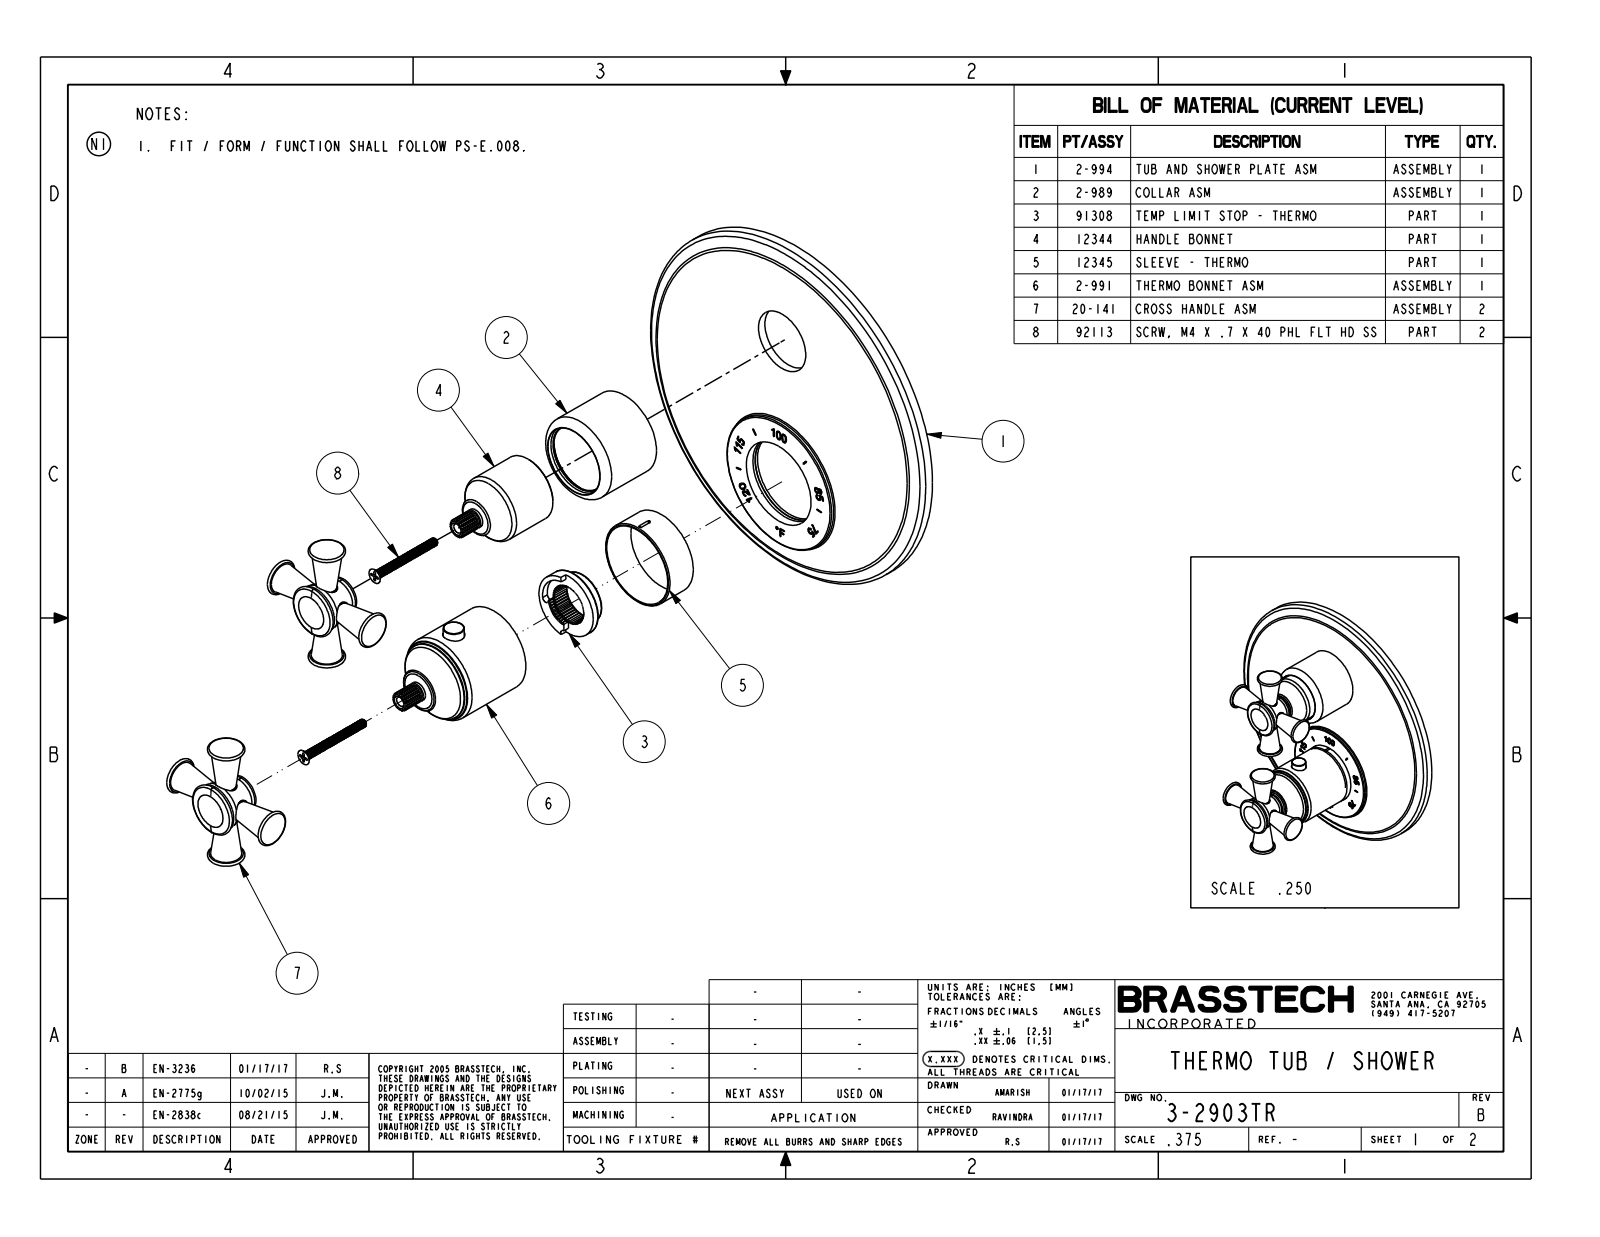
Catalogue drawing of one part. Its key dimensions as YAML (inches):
part_name: "12346_AF0; H-78_2_FEET_AF1; 91678; 2-994_AF0_ASM (+8 more)"
step_written_by: "PRO/ENGINEER BY PARAMETRIC TECHNOLOGY CORPORATION, 2013150 (CONFIG_CONTROL_DESIGN)"
units: inches
bodies: {solids: 23, faces: 2358, planar: 694, cylindrical: 409, other: 1255}
overall_size: [7.087, 7.087, 4.153]
volume: 10.06
surface_area: 275
round_holes:
  - {diameter: 0.186, count: 4}
  - {diameter: 0.11, count: 2}
  - {diameter: 0.19, count: 2}
  - {diameter: 0.4, count: 2}
  - {diameter: 0.057, count: 1}
  - {diameter: 0.079, count: 1}
  - {diameter: 0.1, count: 1}
  - {diameter: 0.126, count: 1}
  - {diameter: 0.276, count: 1}
  - {diameter: 0.276, count: 1}
  - {diameter: 0.406, count: 1}
  - {diameter: 1.015, count: 1}
round_bosses_or_shafts:
  - {diameter: 0.212, count: 4}
  - {diameter: 0.16, count: 4}
  - {diameter: 1.654, count: 2}
  - {diameter: 0.512, count: 2}
  - {diameter: 0.37, count: 2}
  - {diameter: 0.303, count: 2}
  - {diameter: 7.087, count: 1}
  - {diameter: 2, count: 1}
partial_cylinders:
  - {radius: 0.047, count: 3}
  - {radius: 0.169, count: 3}
  - {radius: 0.17, count: 3}
  - {radius: 0.039, count: 2}
  - {radius: 0.082, count: 2}
  - {radius: 0.164, count: 2}
  - {radius: 0.17, count: 2}
face_to_face_distances: [0.08, 0.163, 0.083, 0.253, 0.17, 0.09, 0.185, 0.268, 0.348, 0.438]
hole_center_spacings: [0.367, 0.554, 1.019, 1.022, 1.036, 1.403, 1.572, 1.574]
